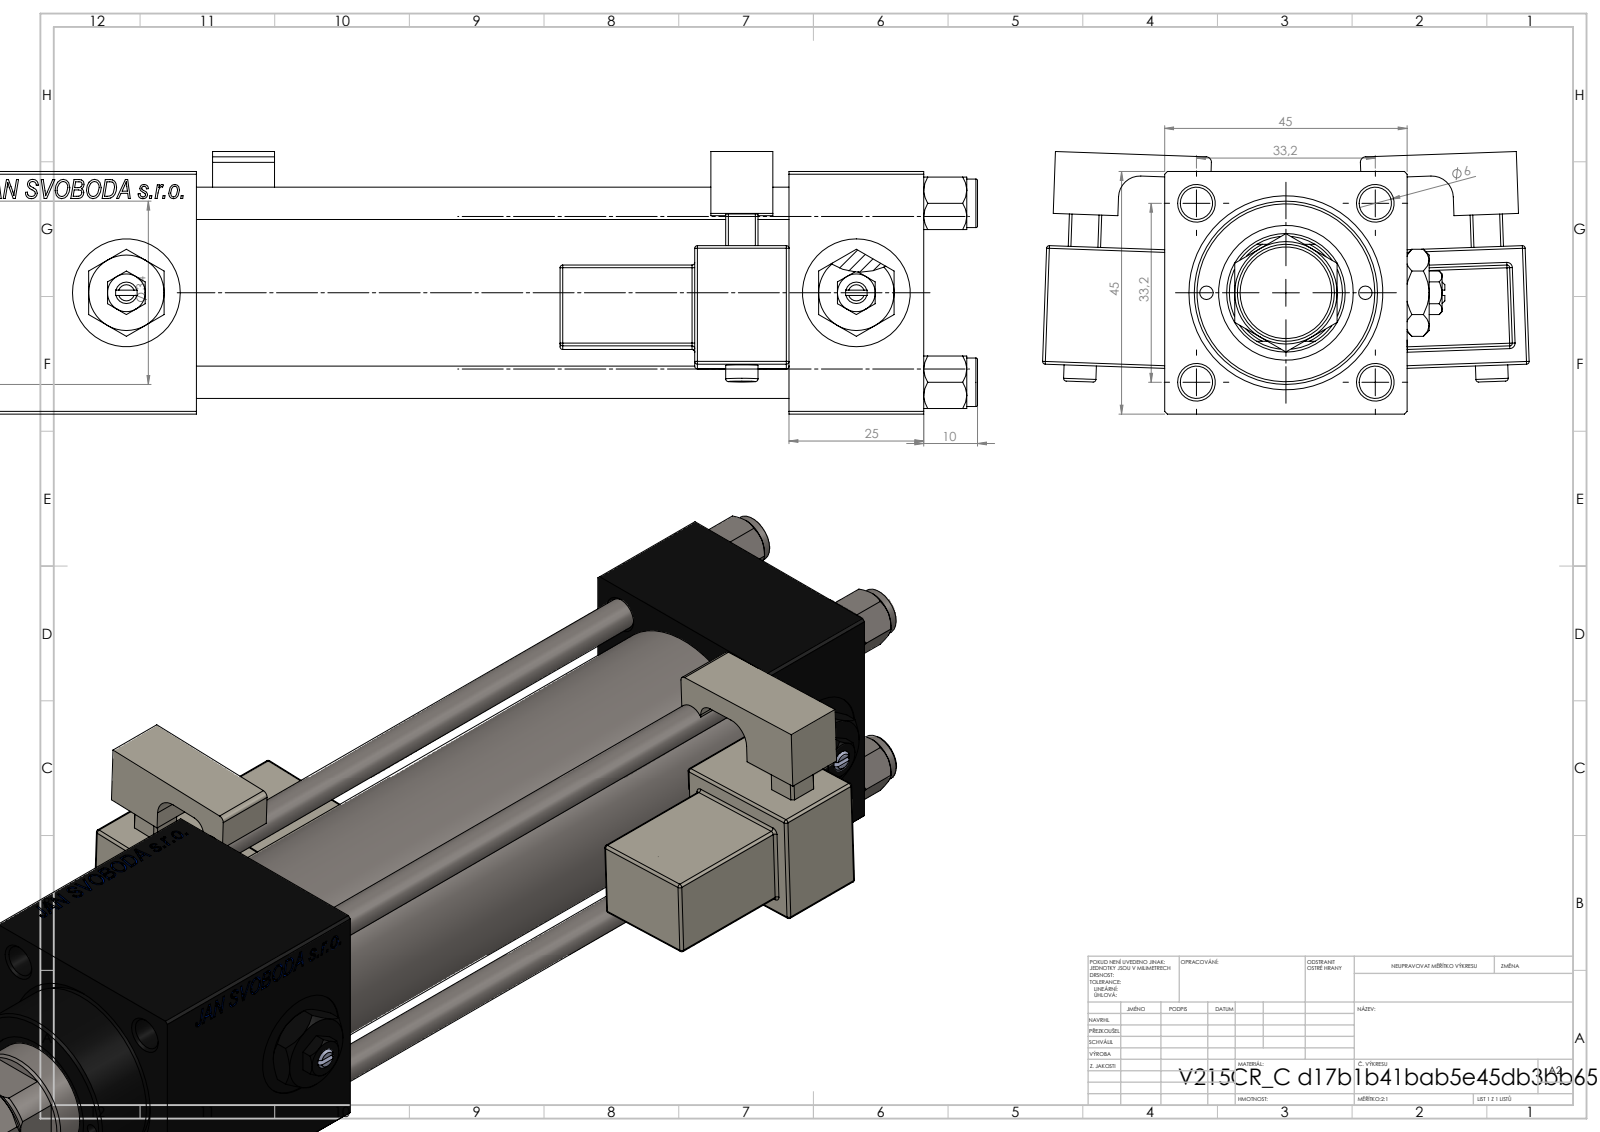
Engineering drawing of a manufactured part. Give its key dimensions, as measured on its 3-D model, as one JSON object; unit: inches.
{"part_name": "NUT_M5_C; Zatka_pro_OIL_PORT; V215CR_MSU; V215CR_C_Body (+4 more)", "step_written_by": "SolidWorks 2019 (CONFIG_CONTROL_DESIGN)", "units": "inches", "bodies": {"solids": 16, "faces": 1464, "planar": 652, "cylindrical": 166, "other": 646}, "overall_size": [9.882, 3.556, 1.918], "volume_in3": 18.69, "surface_area_in2": 170.5, "round_holes": [[0.236, 4], [0.098, 2], [0.276, 2], [0.518, 2], [0.787, 2], [0.413, 1], [0.866, 1], [0.945, 1], [0.984, 1], [1.26, 1], [1.299, 1]], "round_bosses_or_shafts": [[0.354, 4], [0.236, 2], [1.496, 1], [1.339, 1], [0.709, 1], [0.433, 1]], "partial_cylinders_radius": [[0.02, 48], [0.039, 2], [0.098, 2], [0.157, 2], [0.413, 1]], "face_to_face_distances": [1.772, 0.984, 0.118, 5.315, 4.331, 7.205, 0.905, 3.642, 6.22, 1.764], "hole_center_spacings": [0.657, 0.924, 1.307, 1.396, 0.581, 1.848, 1.161, 5.335]}
